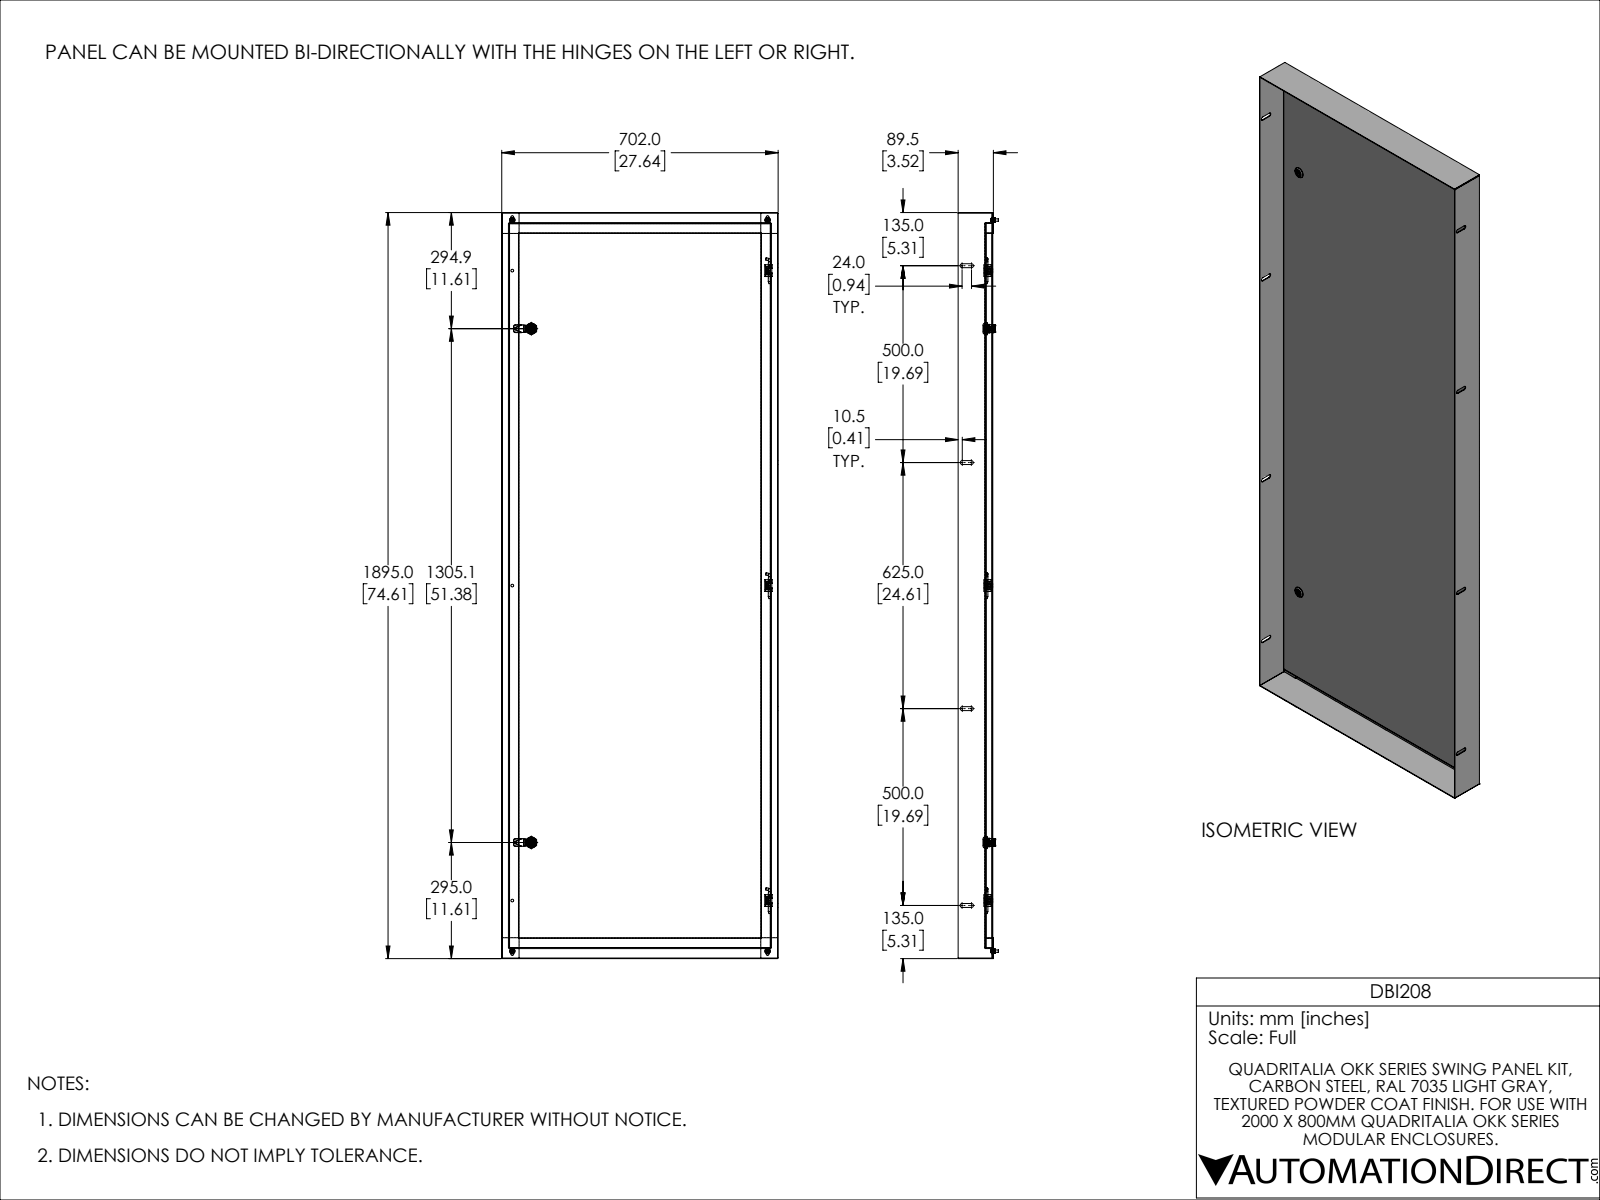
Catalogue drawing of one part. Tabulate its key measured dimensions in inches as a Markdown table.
| quantity | value |
| --- | --- |
| part name | DBI208 |
| STEP written by | SolidWorks 2021 (AUTOMOTIVE_DESIGN) |
| units | inches |
| bodies | 36 solids, 978 faces (603 planar, 253 cylindrical, 122 other) |
| overall size | 74.606 × 27.638 × 4.035 |
| volume | 233.8 in³ |
| surface area | 6 555 in² |
| round holes (diameter × count) | 0.276 × 10, 0.194 × 3, 0.205 × 3, 0.161 × 2, 0.197 × 2, 0.394 × 2, 0.402 × 2, 0.634 × 2, 0.802 × 2, 0.194 × 1, 0.244 × 1, 0.248 × 1 |
| round bosses / shafts (diameter × count) | 0.236 × 8, 0.551 × 4, 0.512 × 4, 1.102 × 2, 0.866 × 2, 0.78 × 2, 0.63 × 2, 0.598 × 2 |
| partial cylindrical surfaces (radius × count) | 0.02 × 51, 0.008 × 10, 0.197 × 9, 0.138 × 8, 0.157 × 8, 0.03 × 4, 0.087 × 4, 0.108 × 4 |
| main face-to-face distances | 0.079, 0.059, 27.579, 0.728, 0.807, 0.748, 0.669, 27.638, 27.52, 74.547 |
| hole center spacings | 31.496, 36.555, 68.051, 25.531, 62.992, 5.059, 26.028, 40.544 |
